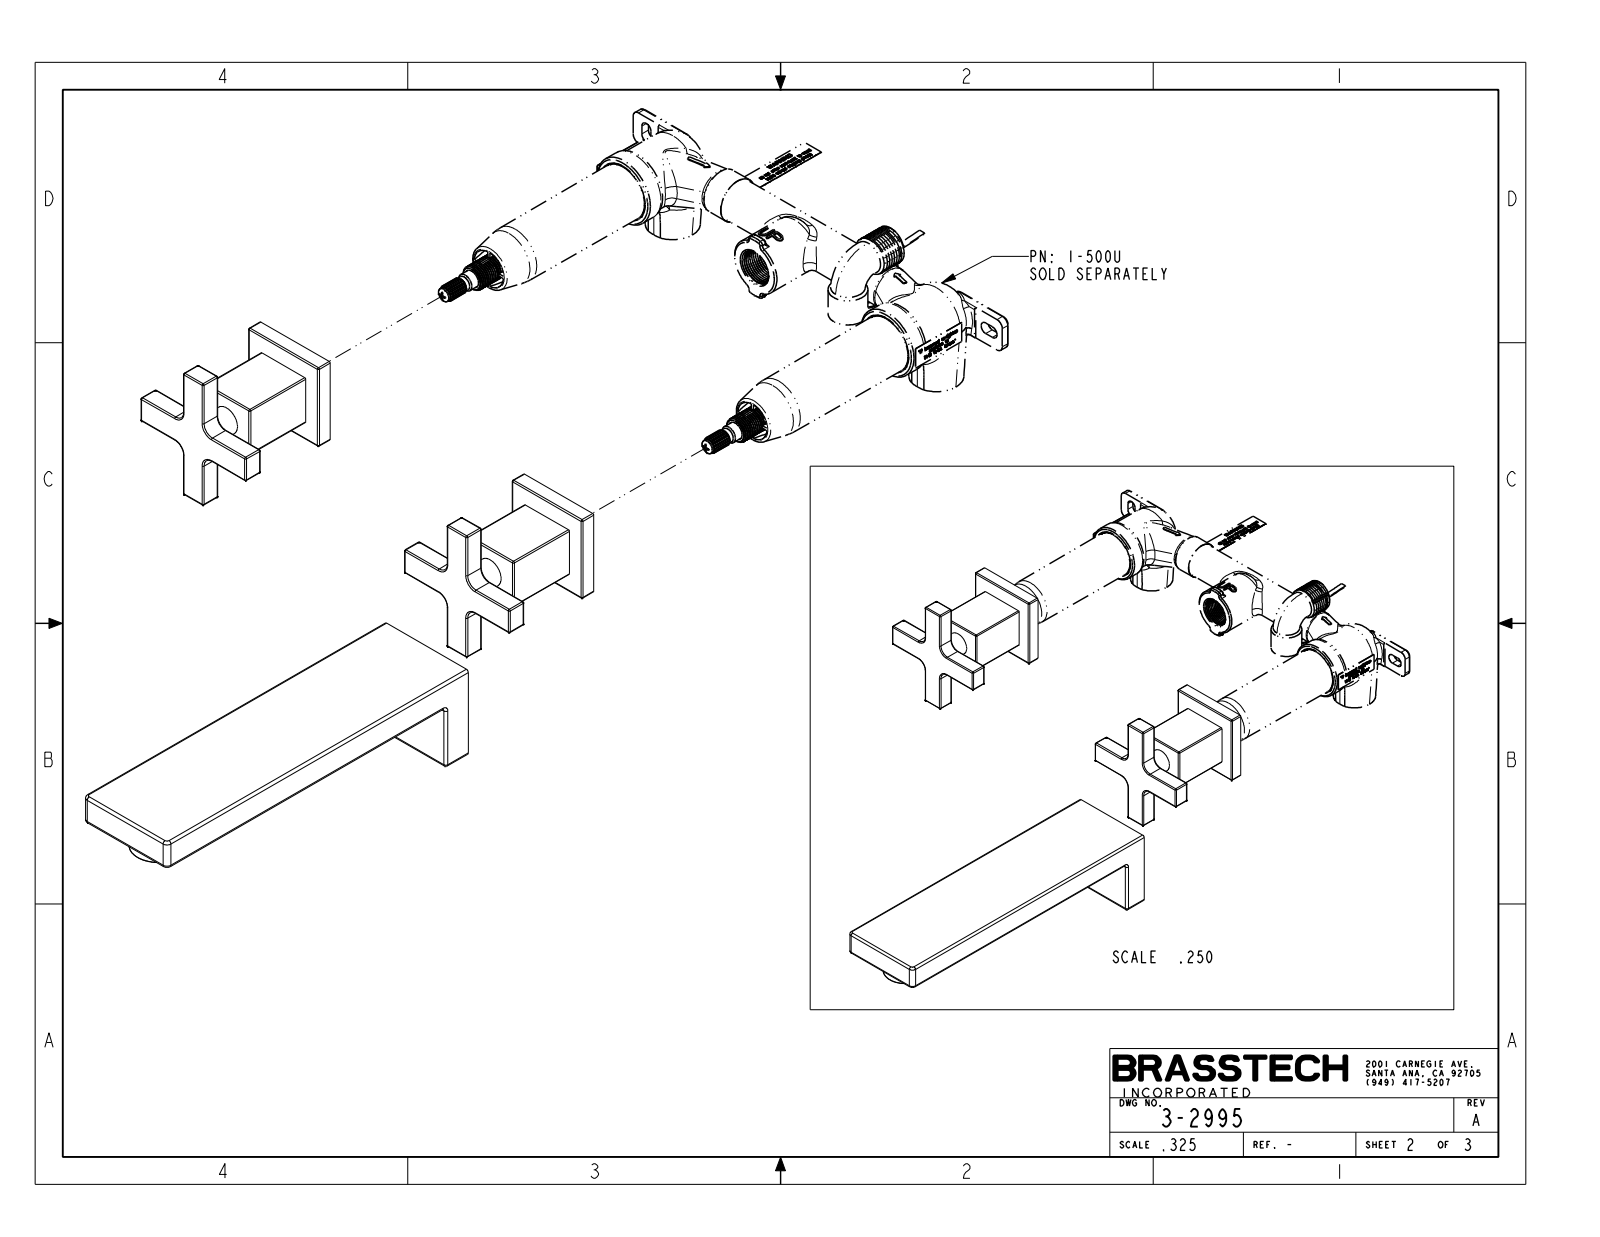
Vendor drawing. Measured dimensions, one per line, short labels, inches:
name: 3-2995_SW0001
written by: CREO PARAMETRIC BY PTC INC, 2018400 (AUTOMOTIVE_DESIGN)
unit: in
bodies: 3 solids, 273 faces (63 planar, 132 cylindrical, 78 other)
size: 11.015 × 9.438 × 8.67
volume: 30.46 in³; area: 136.9 in²
bosses: 2× ⌀0.65, 2× ⌀0.523, 1× ⌀1.8, 1× ⌀1.297, 1× ⌀1.25
rounds: 68× R0.03, 11× R0.06, 8× R0.25, 2× R0.118, 1× R0.08
face distances: 0.67, 3.046, 2.5, 2.596, 0.45, 0.35, 2.246, 2.696, 7.875, 4.99
